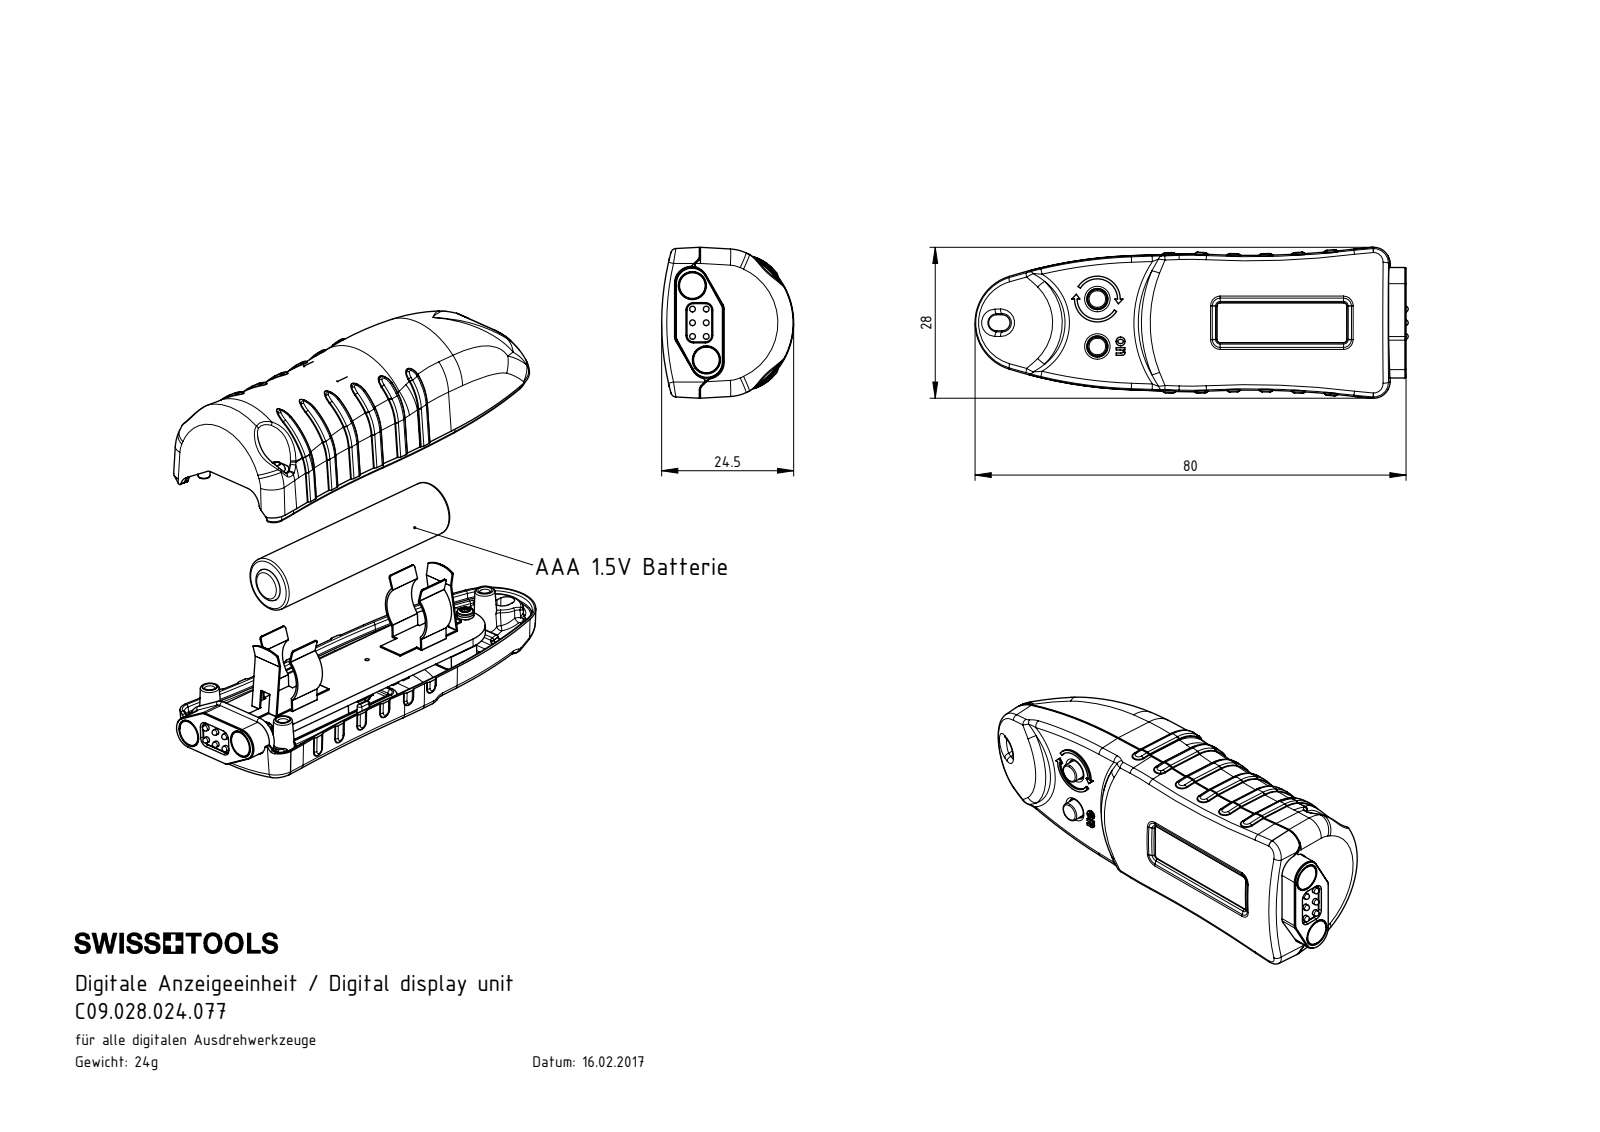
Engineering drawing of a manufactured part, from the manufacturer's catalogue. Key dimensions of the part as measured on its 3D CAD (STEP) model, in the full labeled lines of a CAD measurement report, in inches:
Part name (STEP PRODUCT): Display-1; 22 x 8 WN 5451 6IP; C09.028.024.077; EL1-DA3.BGK.077_Ohne Batterien (+8 more)
STEP written by: SolidWorks 2017 (CONFIG_CONTROL_DESIGN)
Units: inches
Bodies: 26 solids, 2668 faces (578 planar, 464 cylindrical, 1626 other)
Overall size (bounding box): 3.165 × 1.102 × 0.965
Volume: 1.268 in³ · Surface area: 35.97 in²
Round holes (diameter × count): ⌀0.059 ×3, ⌀0.074 ×3, ⌀0.079 ×3, ⌀0.098 ×3, ⌀0.205 ×2, ⌀0.031 ×1, ⌀0.295 ×1
Round bosses / shafts (diameter × count): ⌀0.054 ×6, ⌀0.042 ×6, ⌀0.031 ×6, ⌀0.189 ×3, ⌀0.126 ×3, ⌀0.089 ×3, ⌀0.079 ×3, ⌀0.055 ×3
Partial cylindrical surfaces — rounded edges, fillets, slot ends (radius × count): R0.016 ×46, R0.02 ×41, R0.004 ×38, R0.008 ×33, R0.012 ×30, R0.006 ×27, R0.024 ×26, R0.006 ×9
Main face-to-face distances: 0.061, 0.02, 0.039, 0.043, 0.024, 0.134, 0.247, 0.186, 0.197, 0.173
Hole centre spacings: 0.17, 0.6, 2.272, 2.29, 2.474, 2.494, 0.205, 0.359
